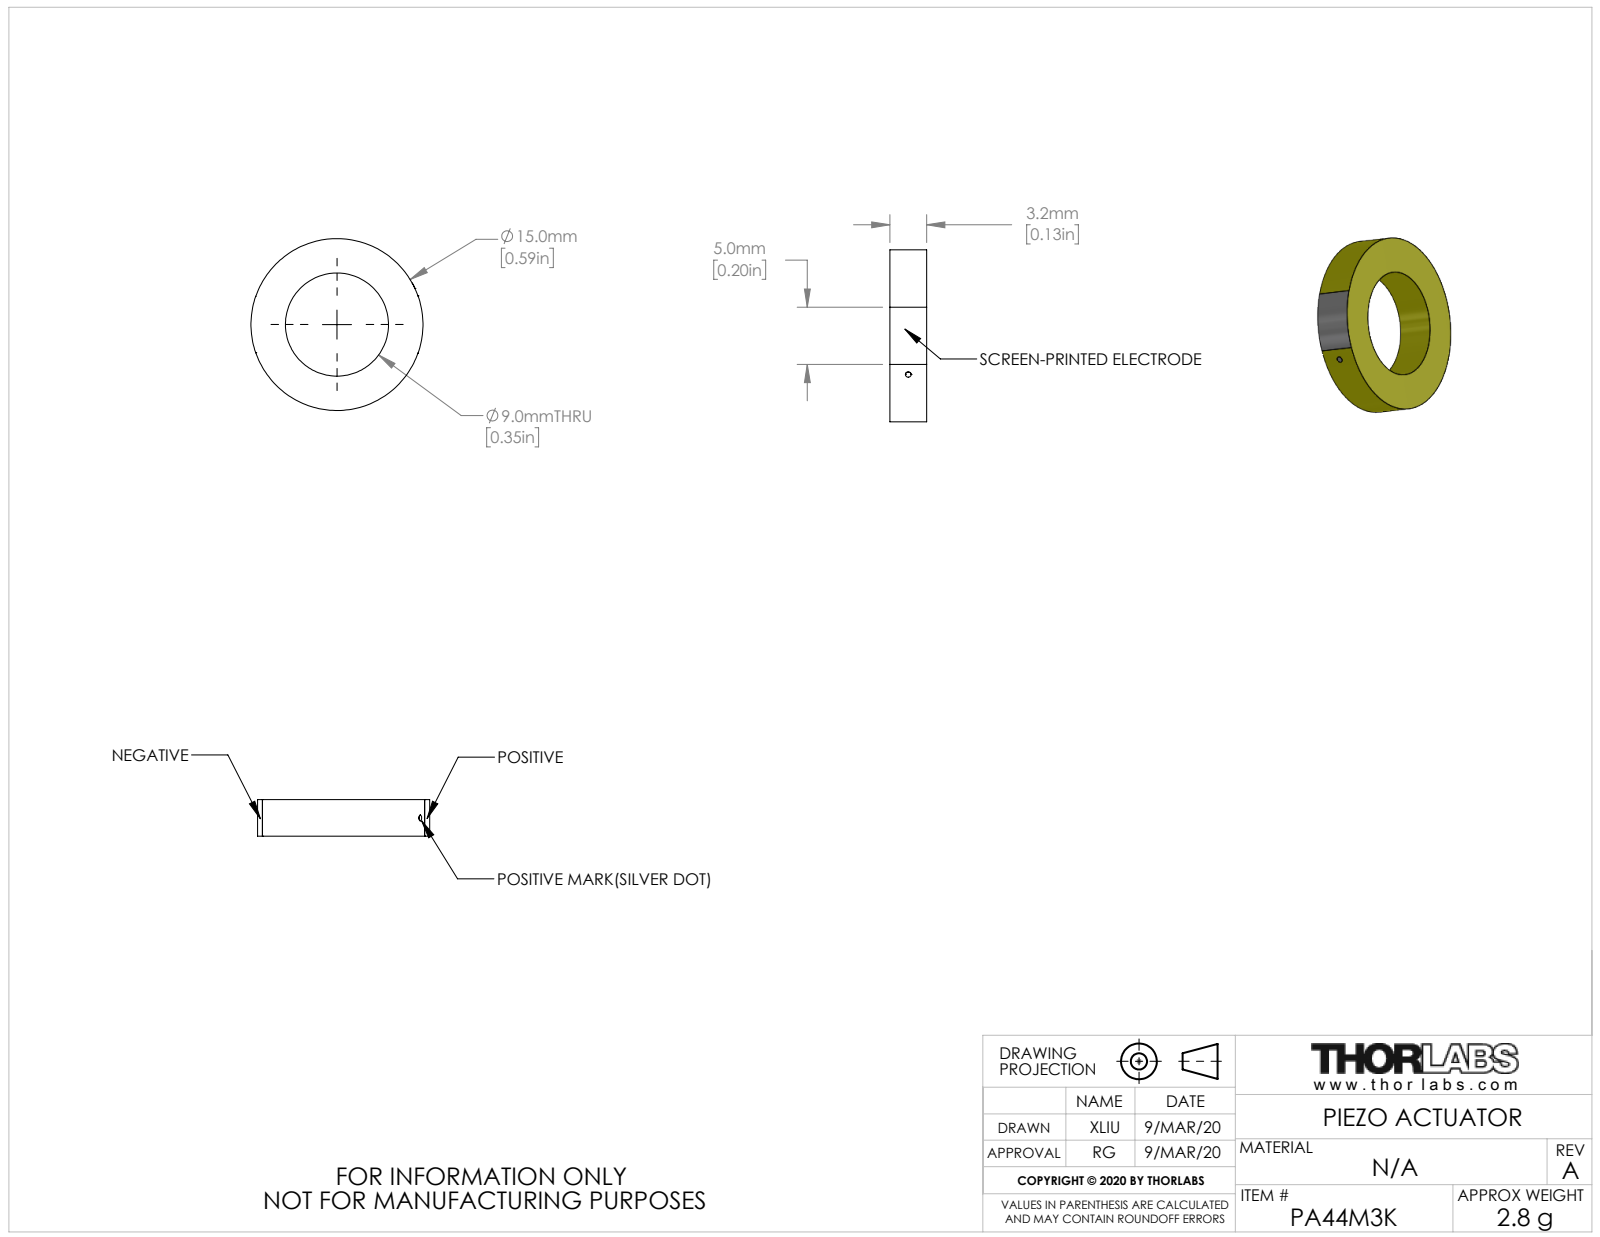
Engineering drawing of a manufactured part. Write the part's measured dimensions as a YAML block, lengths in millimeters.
part_name: "CTN015329"
step_written_by: "SolidWorks 2018 (AUTOMOTIVE_DESIGN)"
units: millimeters
bodies: {solids: 1, faces: 16, planar: 5, cylindrical: 8, other: 3}
overall_size: [15.02, 15, 3.2]
volume: 362
surface_area: 468
round_holes:
  - {diameter: 9, count: 1}
partial_cylinders:
  - {radius: 7.5, count: 1}
  - {radius: 7.51, count: 1}
face_to_face_distances: [3.2]
